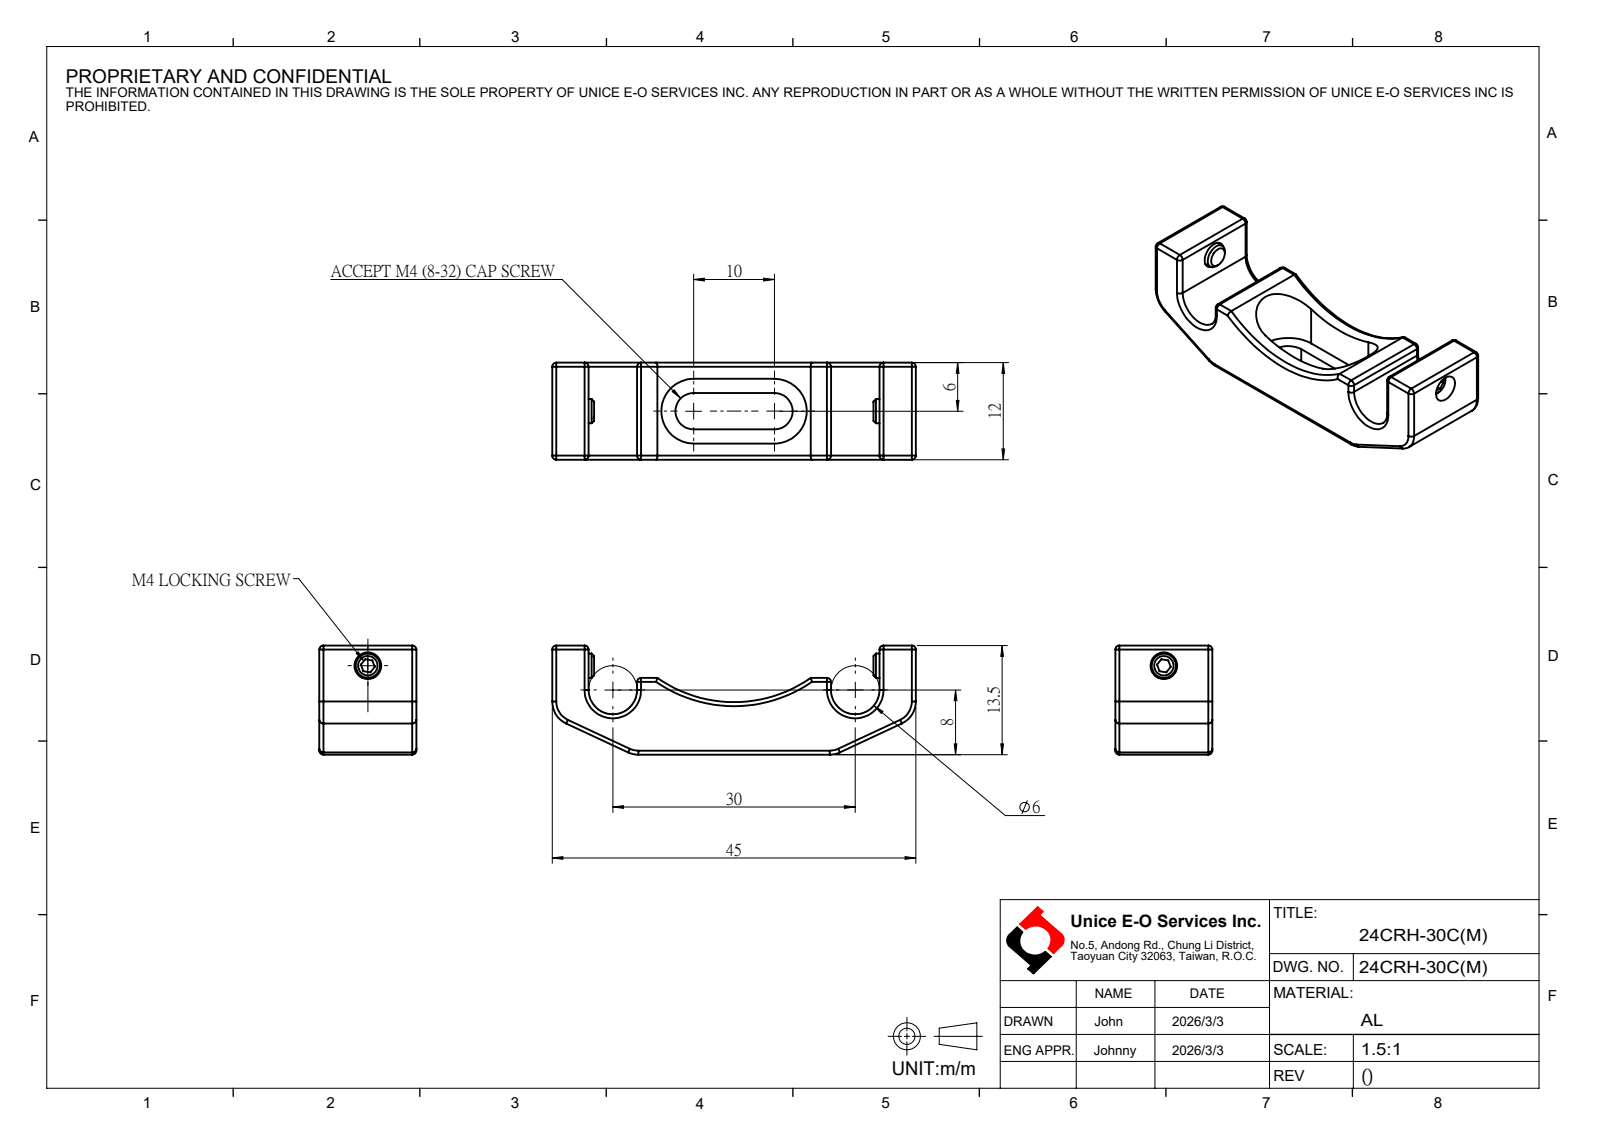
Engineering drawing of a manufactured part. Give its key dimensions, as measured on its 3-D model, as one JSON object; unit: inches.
{"part_name": "24CRH-30C(M)", "step_written_by": "SolidWorks 2024 (CONFIG_CONTROL_DESIGN)", "units": "inches", "bodies": {"solids": 3, "faces": 123, "planar": 38, "cylindrical": 51, "other": 34}, "overall_size": [1.772, 0.531, 0.472], "volume_in3": 0.191, "surface_area_in2": 3.925, "round_holes": [[0.13, 1]], "round_bosses_or_shafts": [[0.118, 1]], "partial_cylinders_radius": [[0.02, 28], [0.118, 6], [0.089, 2], [0.157, 2], [0.65, 1]], "face_to_face_distances": [0.472, 0.177, 0.079, 0.394, 1.594, 0.531, 0.083, 0.449, 1.772, 0.157]}
